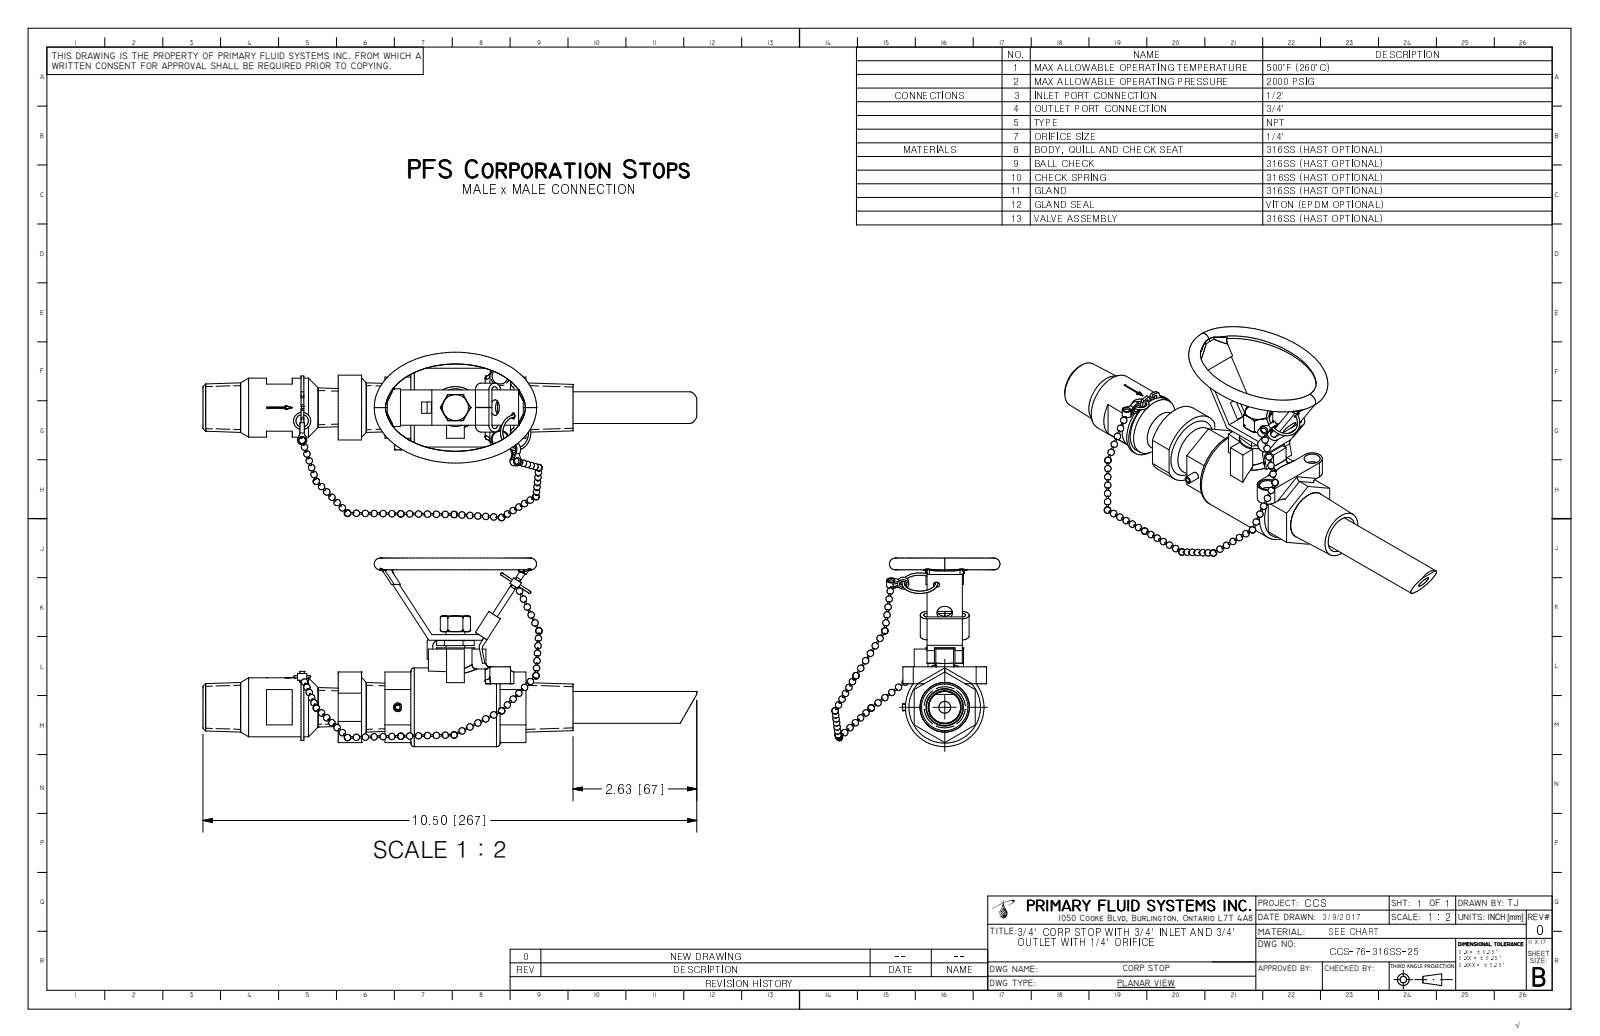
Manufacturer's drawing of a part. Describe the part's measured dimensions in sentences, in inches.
The part is named "CCS-76-316SS-25_R0". Its 3-D file was written by "Autodesk Inventor 2009 (AUTOMOTIVE_DESIGN)". It is 0 solids with 390 faces: 178 planar, 41 cylindrical and 171 other. Overall it measures 10.5 by 4 by 3.574 inches. Round holes: 1 of diameter 0.098, 1 of diameter 0.25, 1 of diameter 0.469. Round bosses or shafts: 1 of diameter 1.67, 1 of diameter 1.343, 1 of diameter 1.25, 1 of diameter 0.8, 1 of diameter 0.675, 1 of diameter 0.4, 1 of diameter 0.15. Partial cylindrical surfaces (rounded edges, fillets, slot ends): 4 of radius 0.075, 2 of radius 0.05, 2 of radius 0.054, 2 of radius 0.145, 2 of radius 0.15, 2 of radius 0.197, 1 of radius 0.125, 1 of radius 0.165. The main face-to-face distances are 1.299, 0.12, 1, 0.15, 1.15, 0.55, 0.275, 1.025, 0.125, 0.12. The hole center spacings are 0.657.
